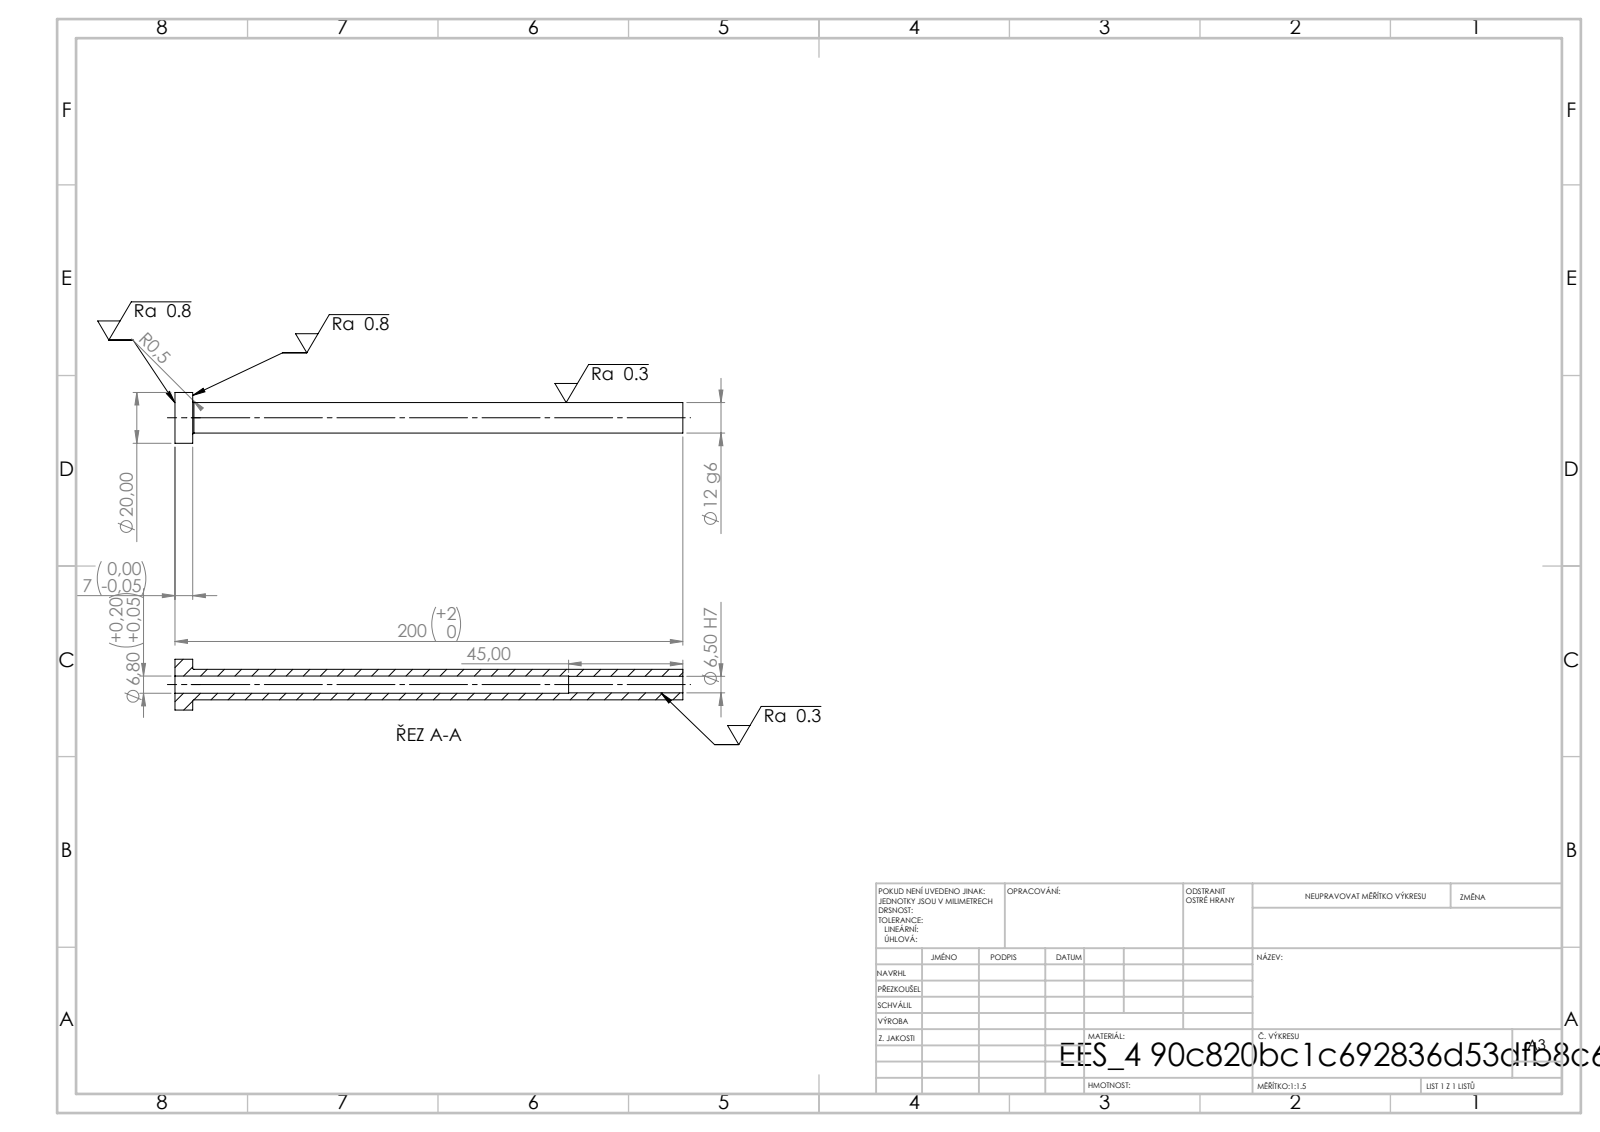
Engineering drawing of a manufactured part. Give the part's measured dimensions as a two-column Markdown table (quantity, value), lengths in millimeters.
| quantity | value |
| --- | --- |
| STEP written by | SolidWorks 2019 (CONFIG_CONTROL_DESIGN) |
| units | millimeters |
| bodies | 1 solid, 14 faces (4 planar, 8 cylindrical, 2 other) |
| overall size | 200 × 20 × 20 |
| volume | 16 907 mm³ |
| surface area | 12 500 mm² |
| round holes (diameter × count) | 6.5 × 1, 6.8 × 1 |
| round bosses / shafts (diameter × count) | 20 × 1, 12 × 1 |
| main face-to-face distances | 7, 200, 193, 155, 148, 45 |
